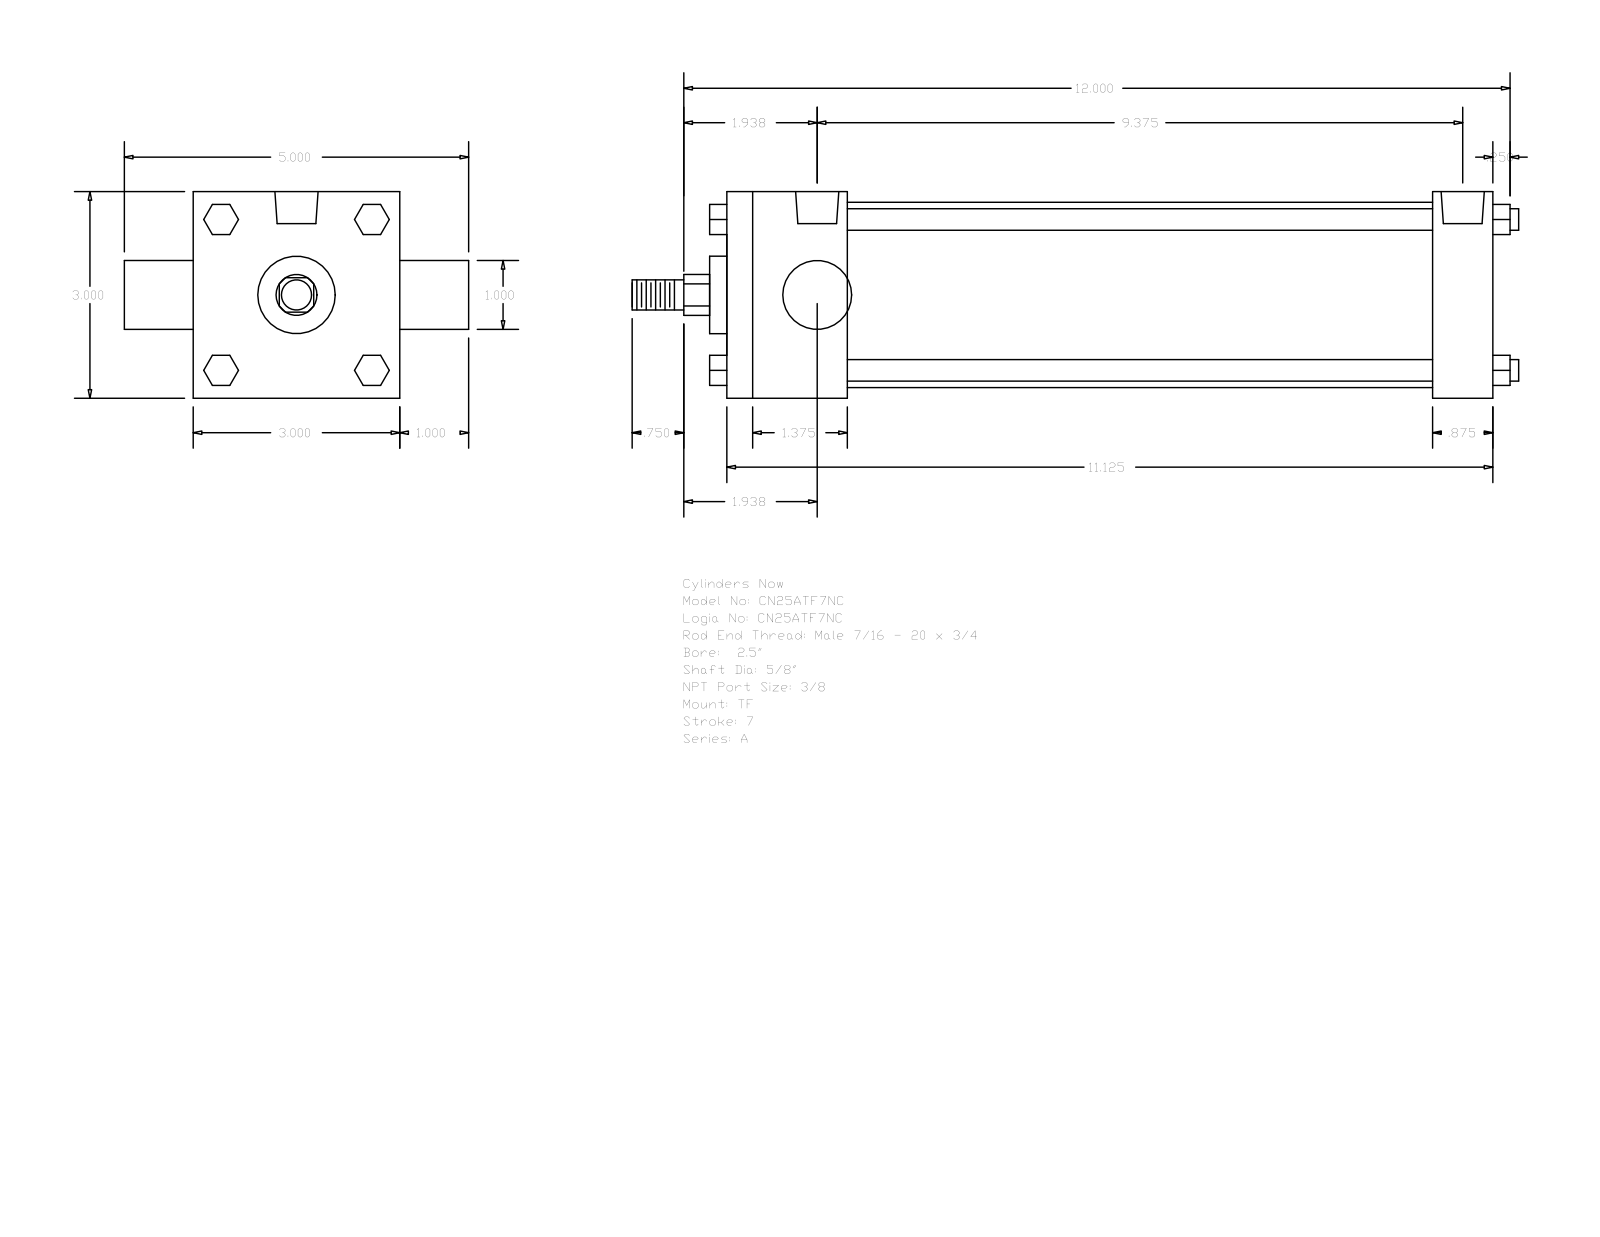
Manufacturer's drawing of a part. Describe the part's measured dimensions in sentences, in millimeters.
The part is named "A_TF__0250_0.625". Its 3-D file was written by "GSSL Pune (CONFIG_CONTROL_DESIGN)". It is 0 solids with 120 faces: 92 planar, 28 cylindrical and 0 other. Overall it measures 327.02 by 127 by 76.2 millimeters. Round holes: 3 of diameter 5.56, 2 of diameter 15.93. Round bosses or shafts: 4 of diameter 7.94, 1 of diameter 68.33, 1 of diameter 28.57, 1 of diameter 25.4, 1 of diameter 15.88, 1 of diameter 11.11. Partial cylindrical surfaces (rounded edges, fillets, slot ends): 1 of radius 7.54. The main face-to-face distances are 76.2, 282.57, 44.45, 260.35, 215.9, 238.12, 22.22, 25.4, 101.6, 6.35. The hole center spacings are 2.38, 240.51, 238.13, 242.89.
